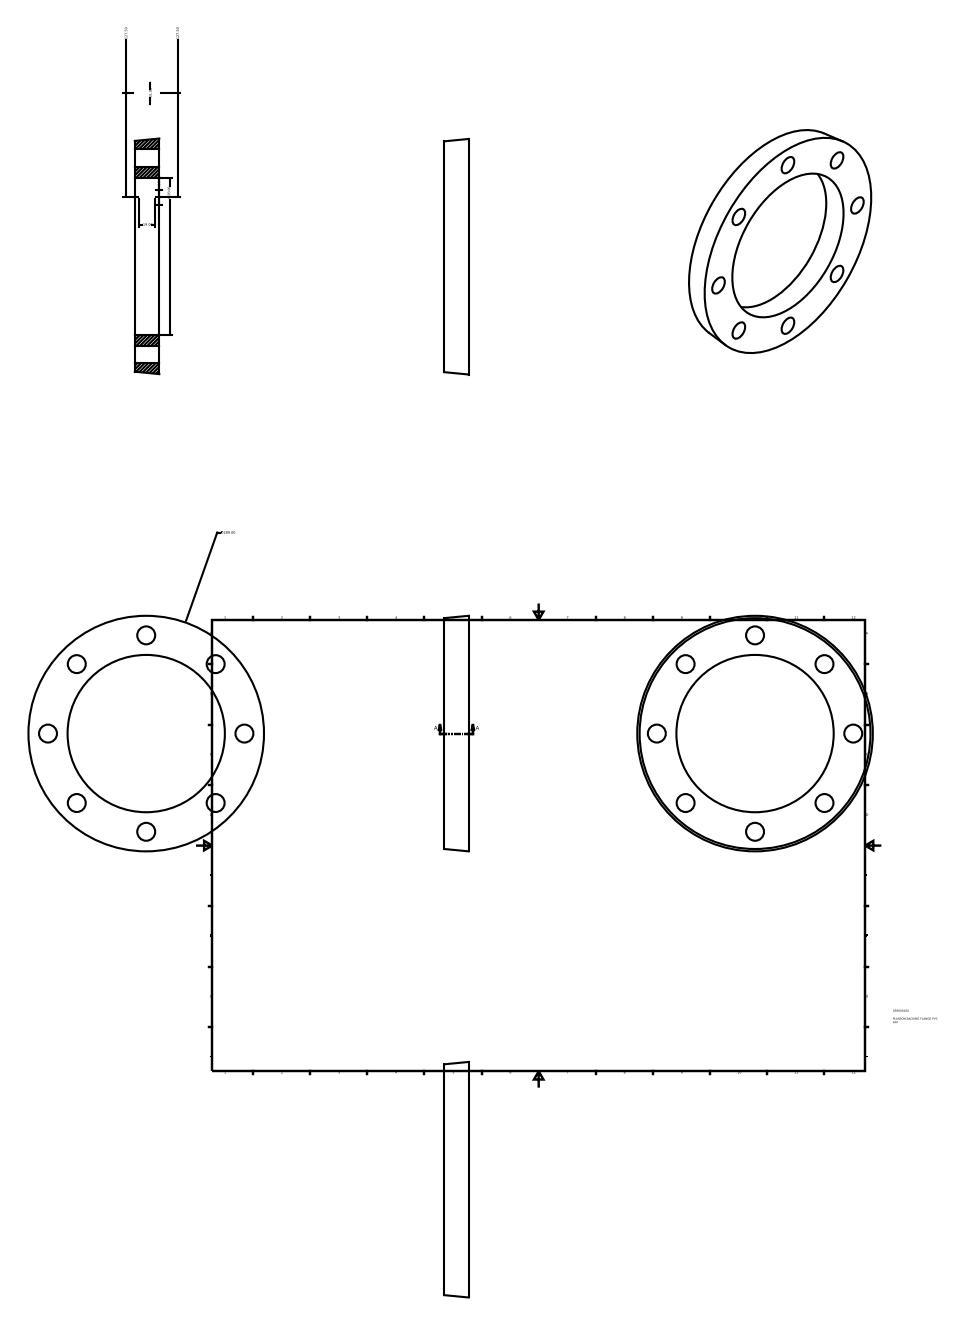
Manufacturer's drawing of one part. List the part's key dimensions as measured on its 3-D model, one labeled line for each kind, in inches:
Part name (STEP PRODUCT): 059000160
STEP written by: Autodesk Inventor 2015 (AUTOMOTIVE_DESIGN)
Units: inches
Bodies: 1 solid, 12 faces (2 planar, 9 cylindrical, 1 other)
Overall size (bounding box): 11.378 × 11.378 × 1.181
Volume: 58.58 in³ · Surface area: 195.1 in²
Round holes (diameter × count): ⌀0.866 ×8, ⌀7.598 ×1
Main face-to-face distances: 1.181
Hole centre spacings: 3.631, 8.766, 4.744, 4.744, 6.709, 6.709, 9.488, 9.489
